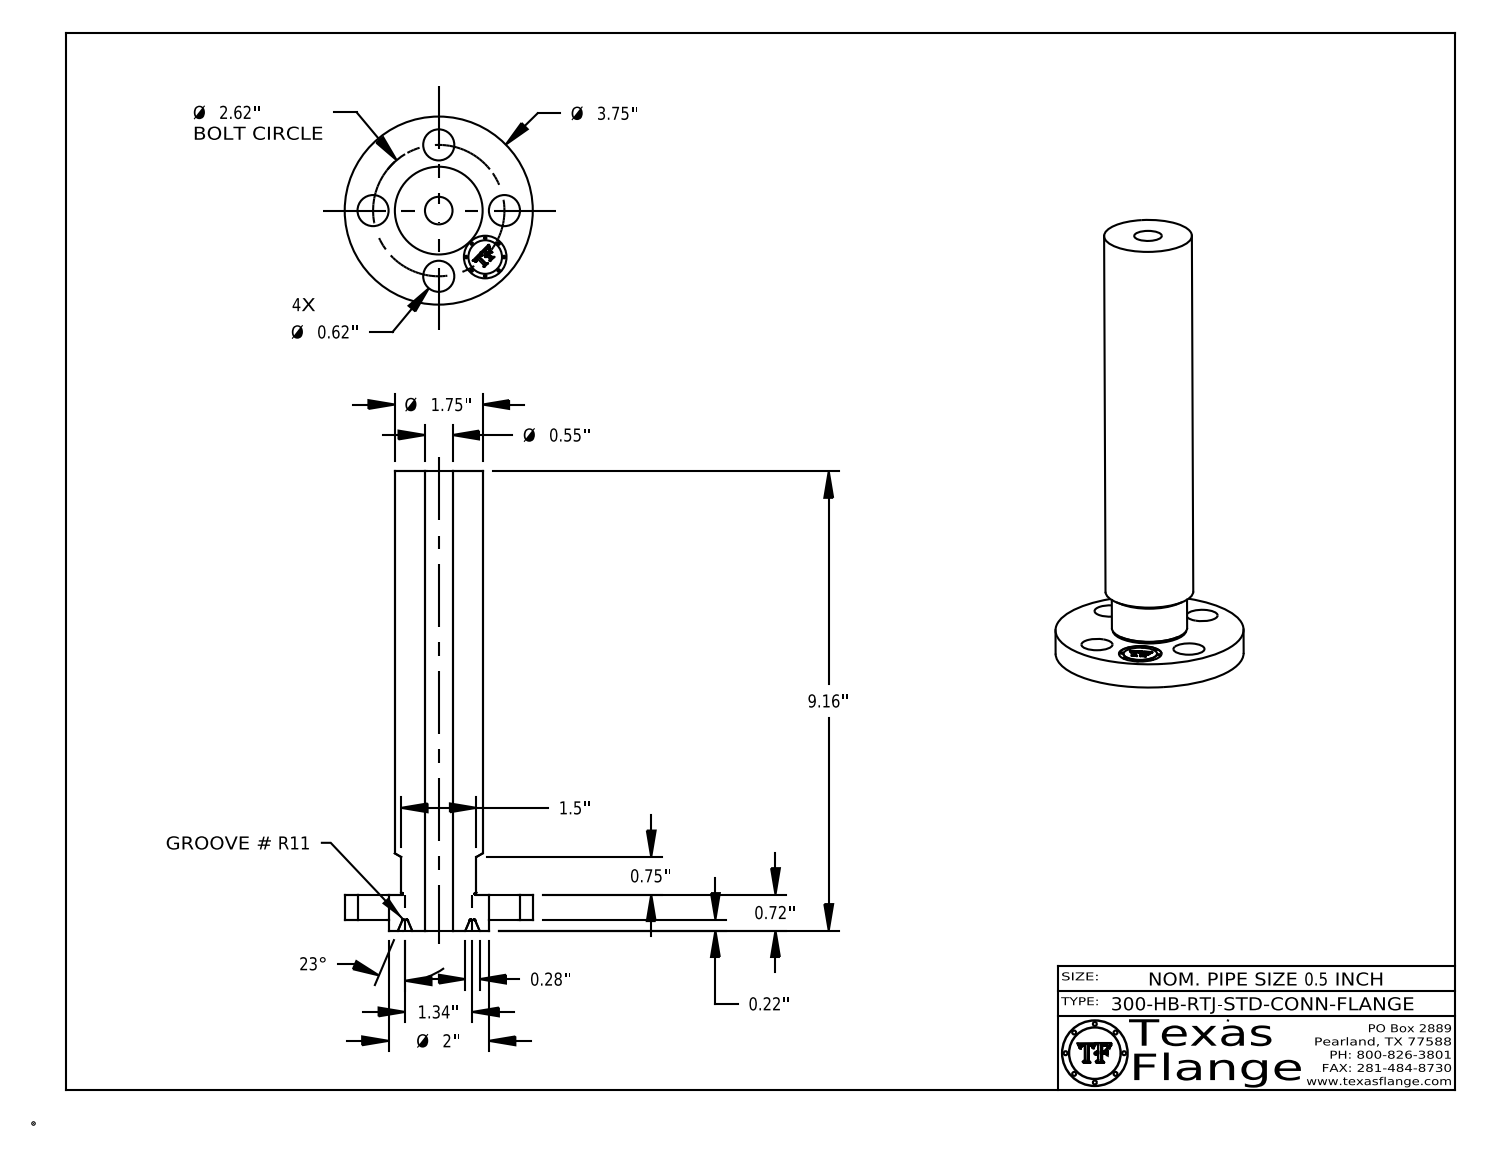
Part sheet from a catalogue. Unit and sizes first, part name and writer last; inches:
Units: inches
Overall size (bounding box): 9.156 × 3.75 × 3.75
Round holes (diameter × count): ⌀0.62 ×4, ⌀0.55 ×1, ⌀0.85 ×1
Round bosses / shafts (diameter × count): ⌀0.051 ×8, ⌀3.75 ×1, ⌀2 ×1, ⌀1.75 ×1, ⌀1.5 ×1, ⌀0.67 ×1
Main face-to-face distances: 0.498, 8.937, 8.44, 0.219, 0.717, 9.156, 0.711, 0.493, 8.445, 0.254
Hole centre spacings: 1.31, 1.852, 1.003, 2.42, 2.62, 1.31
Volume: 23.03 in³ · Surface area: 94.34 in²
Bodies: 1 solid, 423 faces (371 planar, 38 cylindrical, 14 other)
Part name (STEP PRODUCT): 0.5-300-HB-RTJ-STD-CONN-FLANGE
STEP written by: CATIA V5 STEP AP214 (AUTOMOTIVE_DESIGN)
